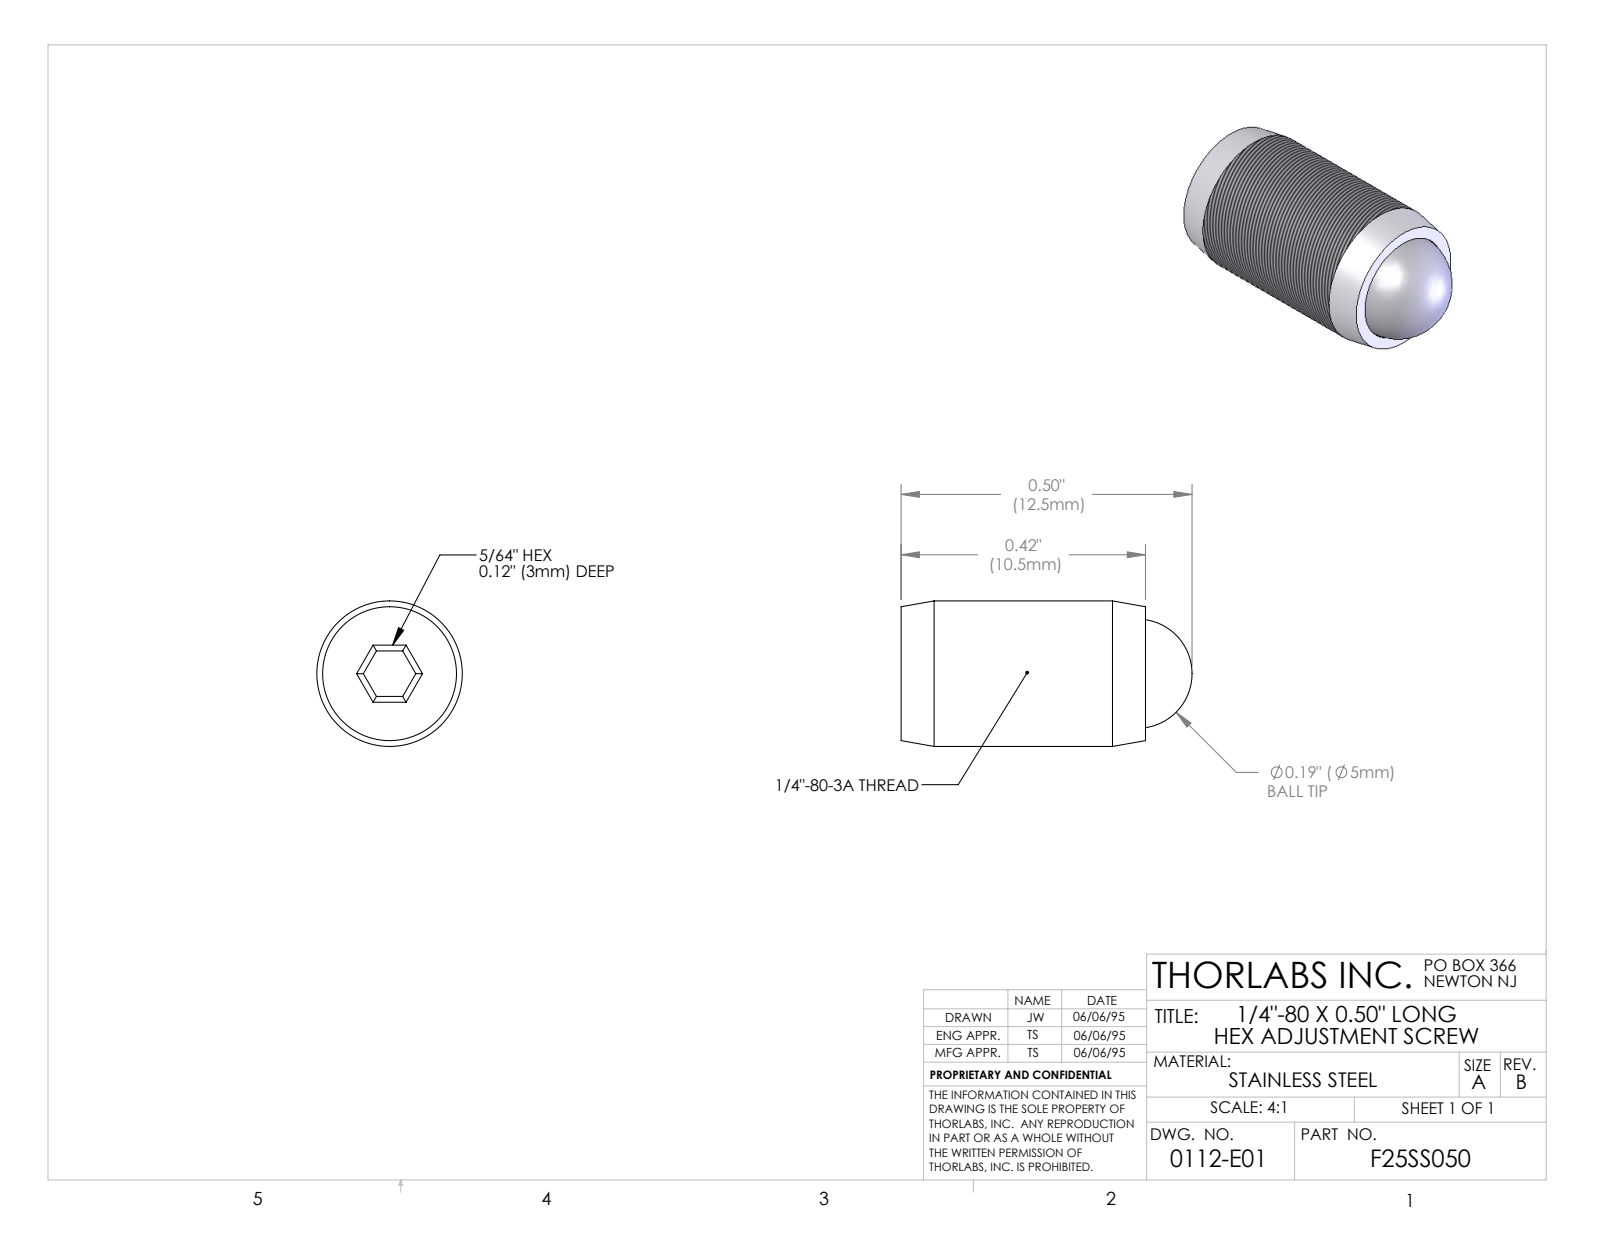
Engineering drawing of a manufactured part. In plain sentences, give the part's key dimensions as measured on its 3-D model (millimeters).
The part is named "0112-E0W". Its 3-D file was written by "SolidWorks 2007 (AUTOMOTIVE_DESIGN)". It is 2 solids with 29 faces: 15 planar, 4 cylindrical and 10 other. Overall it measures 12.7 by 6.35 by 6.35 millimeters. Its volume is 339 cubic millimeters and its surface area 384 square millimeters. Round holes: 1 of diameter 4.78. Round bosses or shafts: 1 of diameter 6.35. The main face-to-face distances are 10.67, 1.99, 3.05, 7.62, 1.98.
